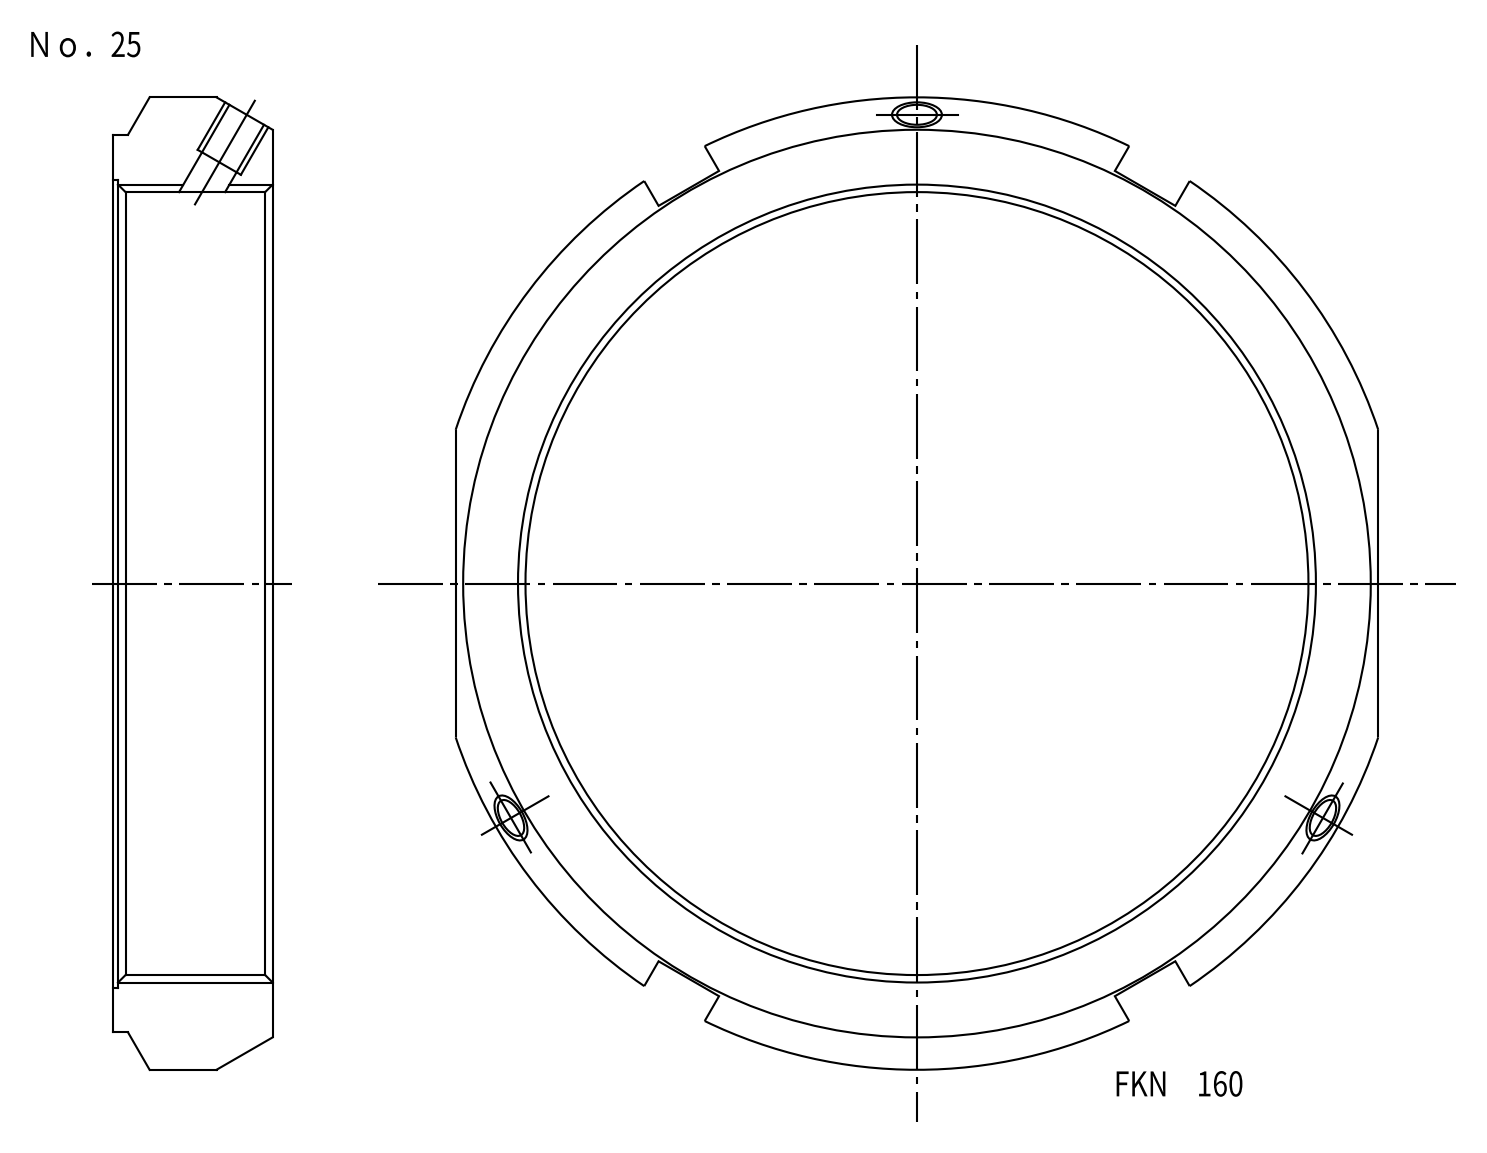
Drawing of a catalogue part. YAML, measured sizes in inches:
part_name: "FKD FKN160"
step_written_by: "Autodesk Inventor LT (CONFIG_CONTROL_DESIGN)"
units: inches
bodies: {solids: 1, faces: 40, planar: 20, cylindrical: 18, other: 2}
overall_size: [7.677, 7.283, 1.26]
volume: 15.25
surface_area: 79.38
round_holes:
  - {diameter: 0.33, count: 3}
  - {diameter: 0.402, count: 3}
  - {diameter: 6.299, count: 1}
  - {diameter: 6.378, count: 1}
round_bosses_or_shafts:
  - {diameter: 7.087, count: 1}
partial_cylinders:
  - {radius: 3.839, count: 1}
face_to_face_distances: [1.26, 7.283, 7.205, 0.059, 1.201, 0.551]
